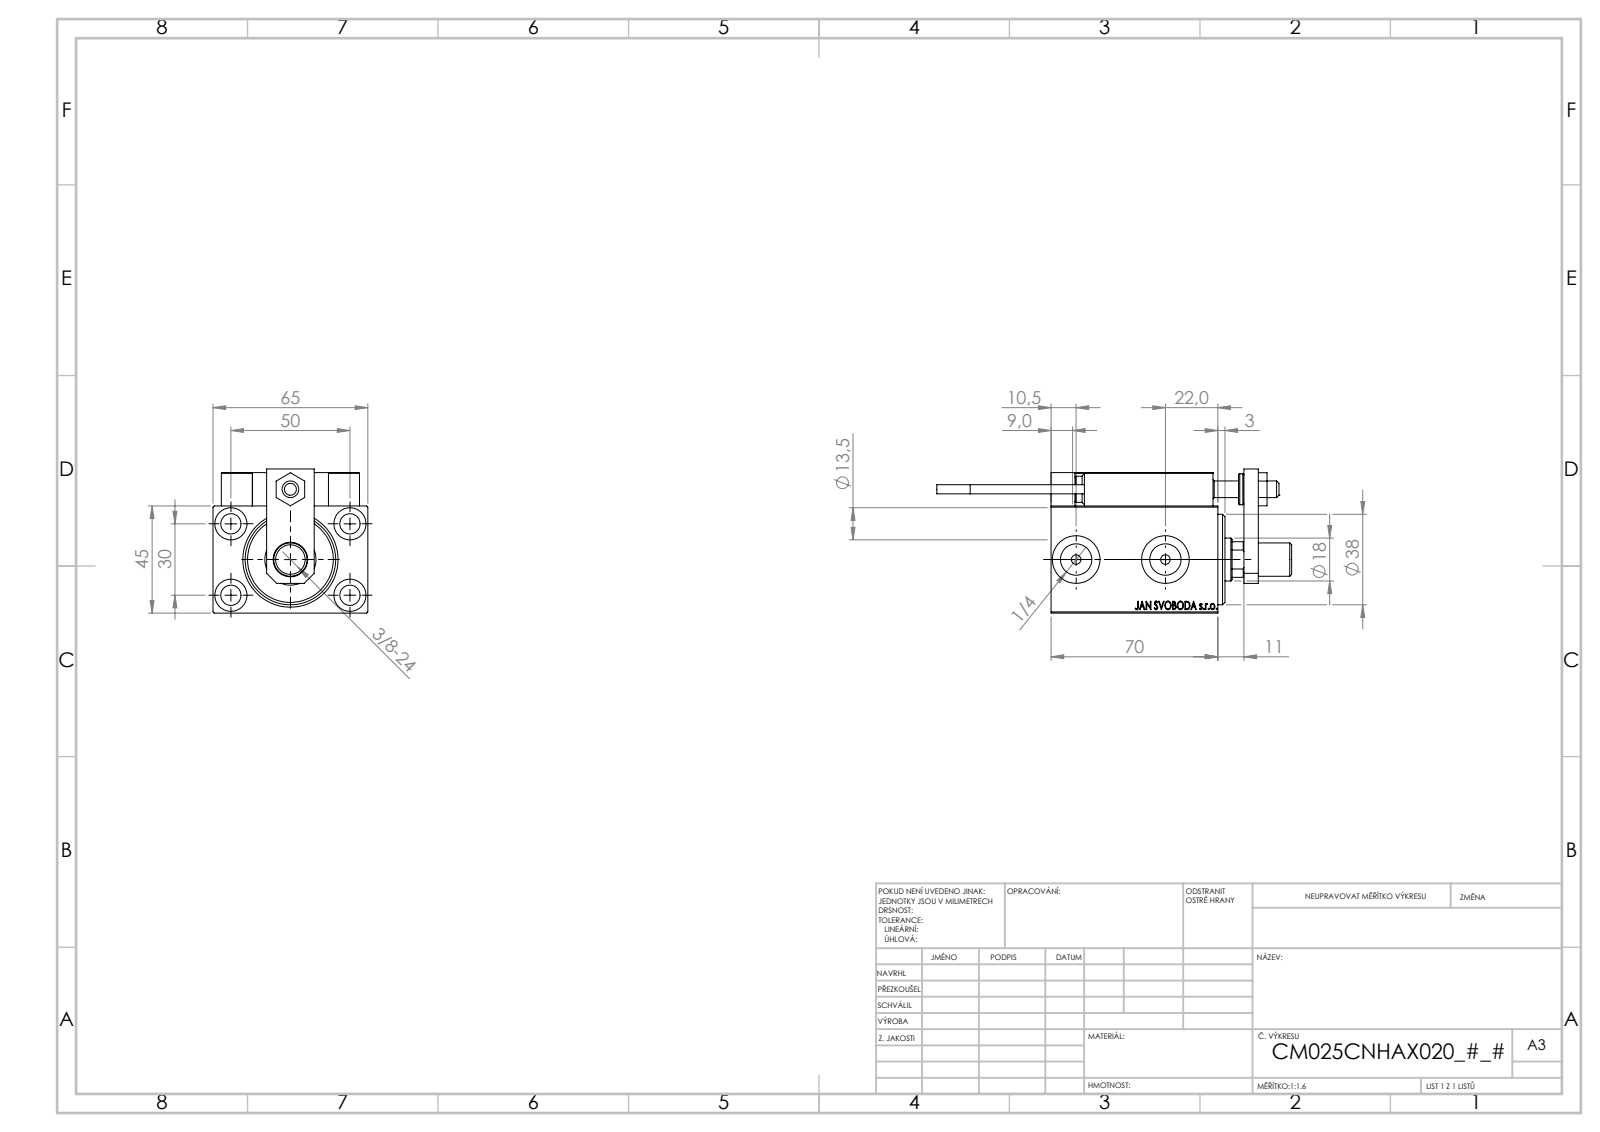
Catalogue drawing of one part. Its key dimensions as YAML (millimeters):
part_name: "KONCOVKA; ALLEN BOLT D8; NUT_D12; V450CM_VC_B (+7 more)"
step_written_by: "SolidWorks 2019 (CONFIG_CONTROL_DESIGN)"
units: millimeters
bodies: {solids: 24, faces: 1295, planar: 563, cylindrical: 192, other: 540}
overall_size: [149, 65, 60.5]
volume: 226080
surface_area: 70361
round_holes:
  - {diameter: 4, count: 6}
  - {diameter: 8, count: 5}
  - {diameter: 8.5, count: 5}
  - {diameter: 3.2, count: 4}
  - {diameter: 13.5, count: 4}
  - {diameter: 5, count: 2}
  - {diameter: 13.16, count: 2}
  - {diameter: 20, count: 2}
  - {diameter: 7, count: 1}
  - {diameter: 14.5, count: 1}
  - {diameter: 18, count: 1}
  - {diameter: 21.5, count: 1}
round_bosses_or_shafts:
  - {diameter: 5, count: 2}
  - {diameter: 3.8, count: 2}
  - {diameter: 14, count: 1}
  - {diameter: 13, count: 1}
  - {diameter: 12, count: 1}
  - {diameter: 11, count: 1}
partial_cylinders:
  - {radius: 0.3, count: 30}
  - {radius: 3, count: 2}
  - {radius: 8.5, count: 1}
face_to_face_distances: [45, 59, 14, 65, 6, 3, 19, 5, 13, 7]
hole_center_spacings: [29.15, 11.37, 20, 22.09, 28.9, 29.59, 29.69, 30]
